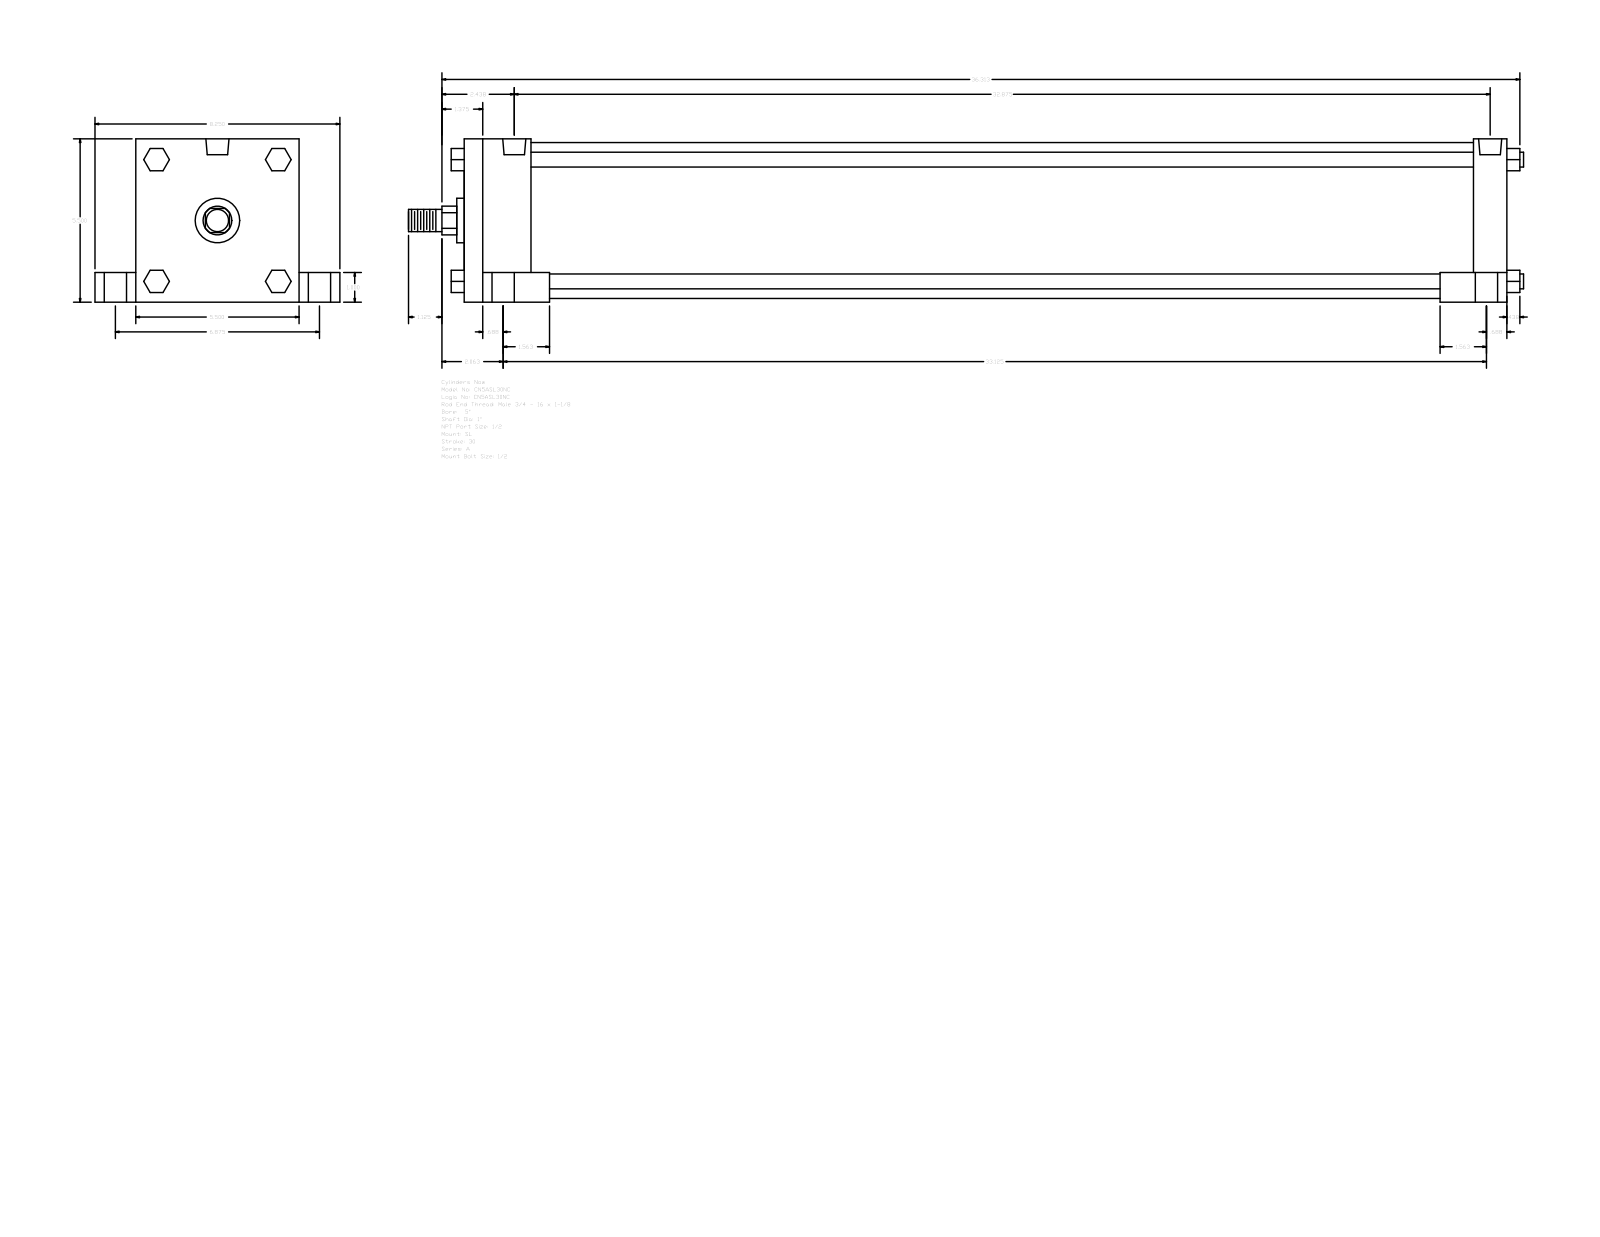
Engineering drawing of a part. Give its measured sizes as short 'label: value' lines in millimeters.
name: A_SL__0500_1
written by: GSSL Pune (CONFIG_CONTROL_DESIGN)
unit: mm
bodies: 0 solids, 150 faces (114 planar, 36 cylindrical, 0 other)
size: 954.09 × 209.55 × 139.7
holes: 4× ⌀8.73, 4× ⌀19.05, 4× ⌀25.4, 2× ⌀19.77
bosses: 4× ⌀12.7, 1× ⌀133.35, 1× ⌀38.1, 1× ⌀25.4, 1× ⌀19.05
rounds: 1× R12.29
face distances: 139.7, 892.18, 57.15, 835.03, 25.4, 114.3, 34.93, 174.63, 863.6, 806.45
hole spacings: 2.39, 87.31, 87.37, 87.83, 88.12, 174.62, 830.25, 832.64
